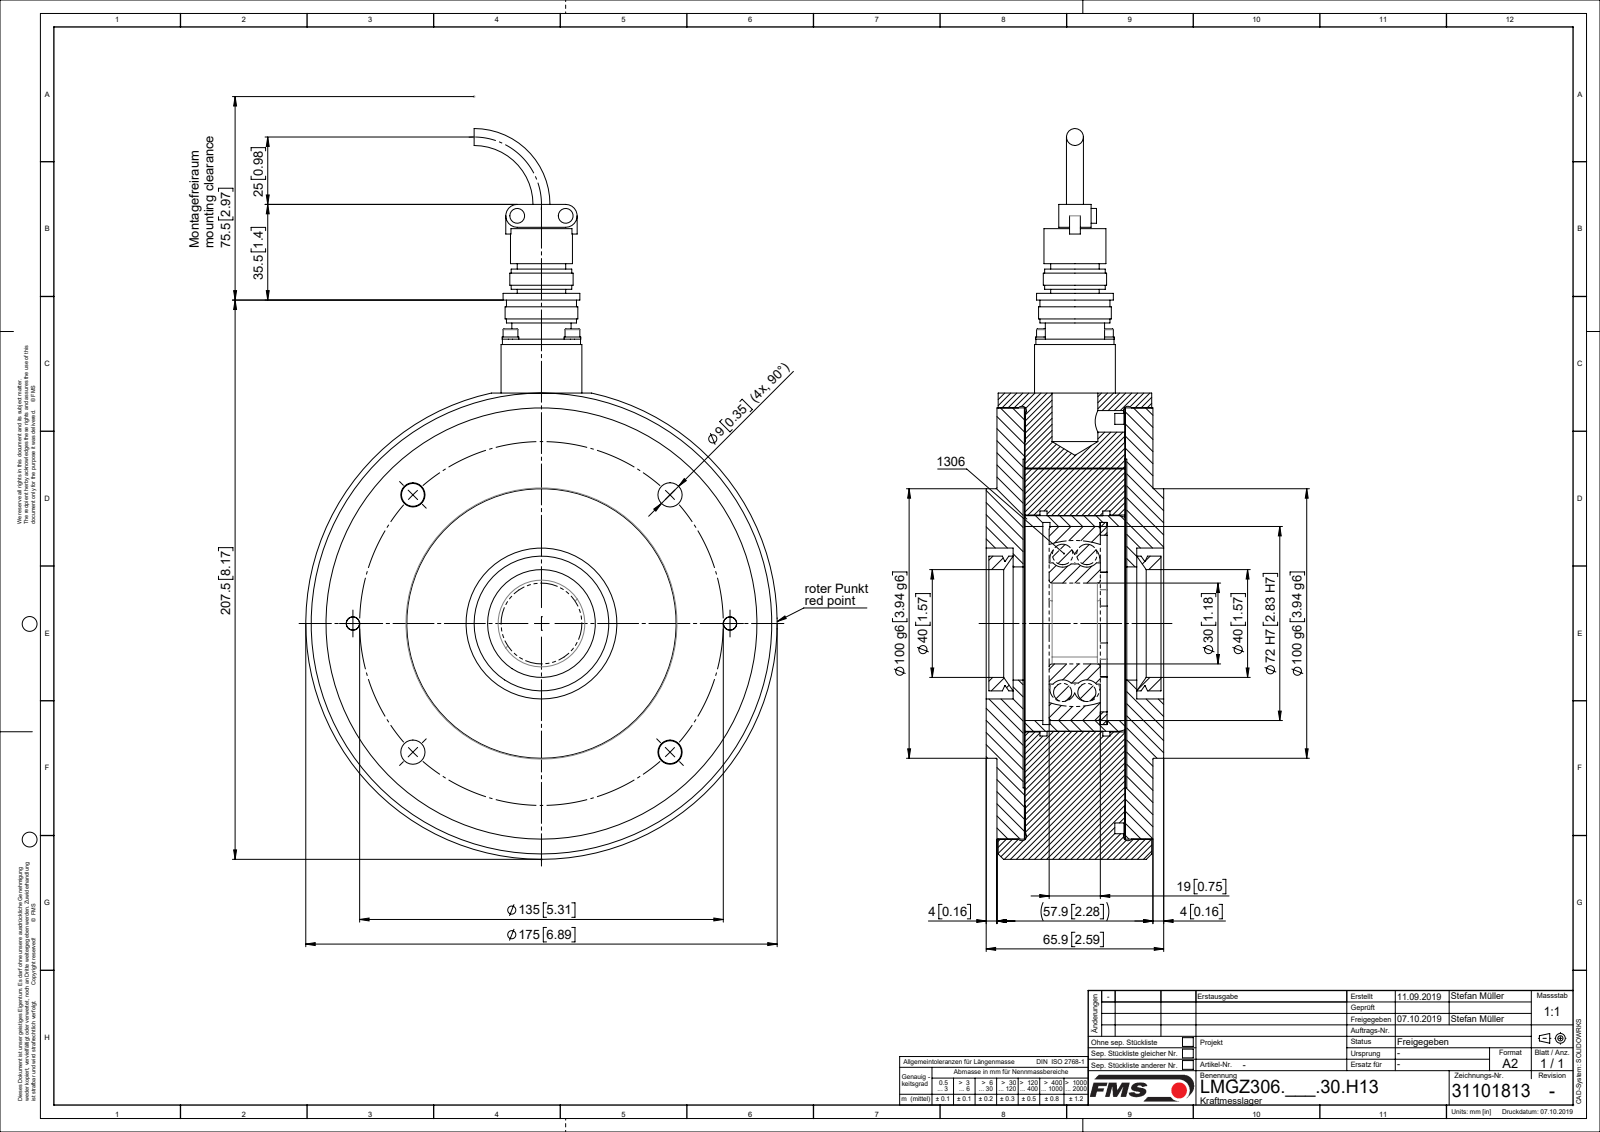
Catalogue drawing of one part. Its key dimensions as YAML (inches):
part_name: "ZEICHNUNG4; L50324_STP; L4974404; TEIL1 (+8 more)"
step_written_by: "Mechanical Desktop 2009 (CONFIG_CONTROL_DESIGN)"
units: inches
bodies: {solids: 23, faces: 429, planar: 108, cylindrical: 249, other: 72}
overall_size: [10.675, 6.89, 2.594]
volume: 79.03
surface_area: 423.5
round_holes:
  - {diameter: 0.102, count: 4}
  - {diameter: 0.126, count: 4}
  - {diameter: 0.134, count: 4}
  - {diameter: 0.354, count: 4}
  - {diameter: 0.197, count: 2}
  - {diameter: 0.26, count: 2}
  - {diameter: 0.315, count: 2}
  - {diameter: 0.335, count: 2}
  - {diameter: 0.433, count: 2}
  - {diameter: 0.394, count: 1}
  - {diameter: 0.669, count: 1}
  - {diameter: 0.906, count: 1}
round_bosses_or_shafts:
  - {diameter: 0.217, count: 6}
  - {diameter: 0.244, count: 4}
  - {diameter: 0.118, count: 4}
  - {diameter: 0.098, count: 4}
  - {diameter: 0.394, count: 2}
  - {diameter: 0.236, count: 2}
  - {diameter: 6.89, count: 1}
  - {diameter: 6.299, count: 1}
partial_cylinders:
  - {radius: 0.167, count: 2}
  - {radius: 0.295, count: 2}
face_to_face_distances: [1.467, 1.496, 0.402, 0.411, 1.868, 1.878, 1.457, 1.486, 0.02, 0.382]
hole_center_spacings: [0.64, 0.906, 1.918, 2.074, 2.657, 3.758, 4.549, 5.002]
